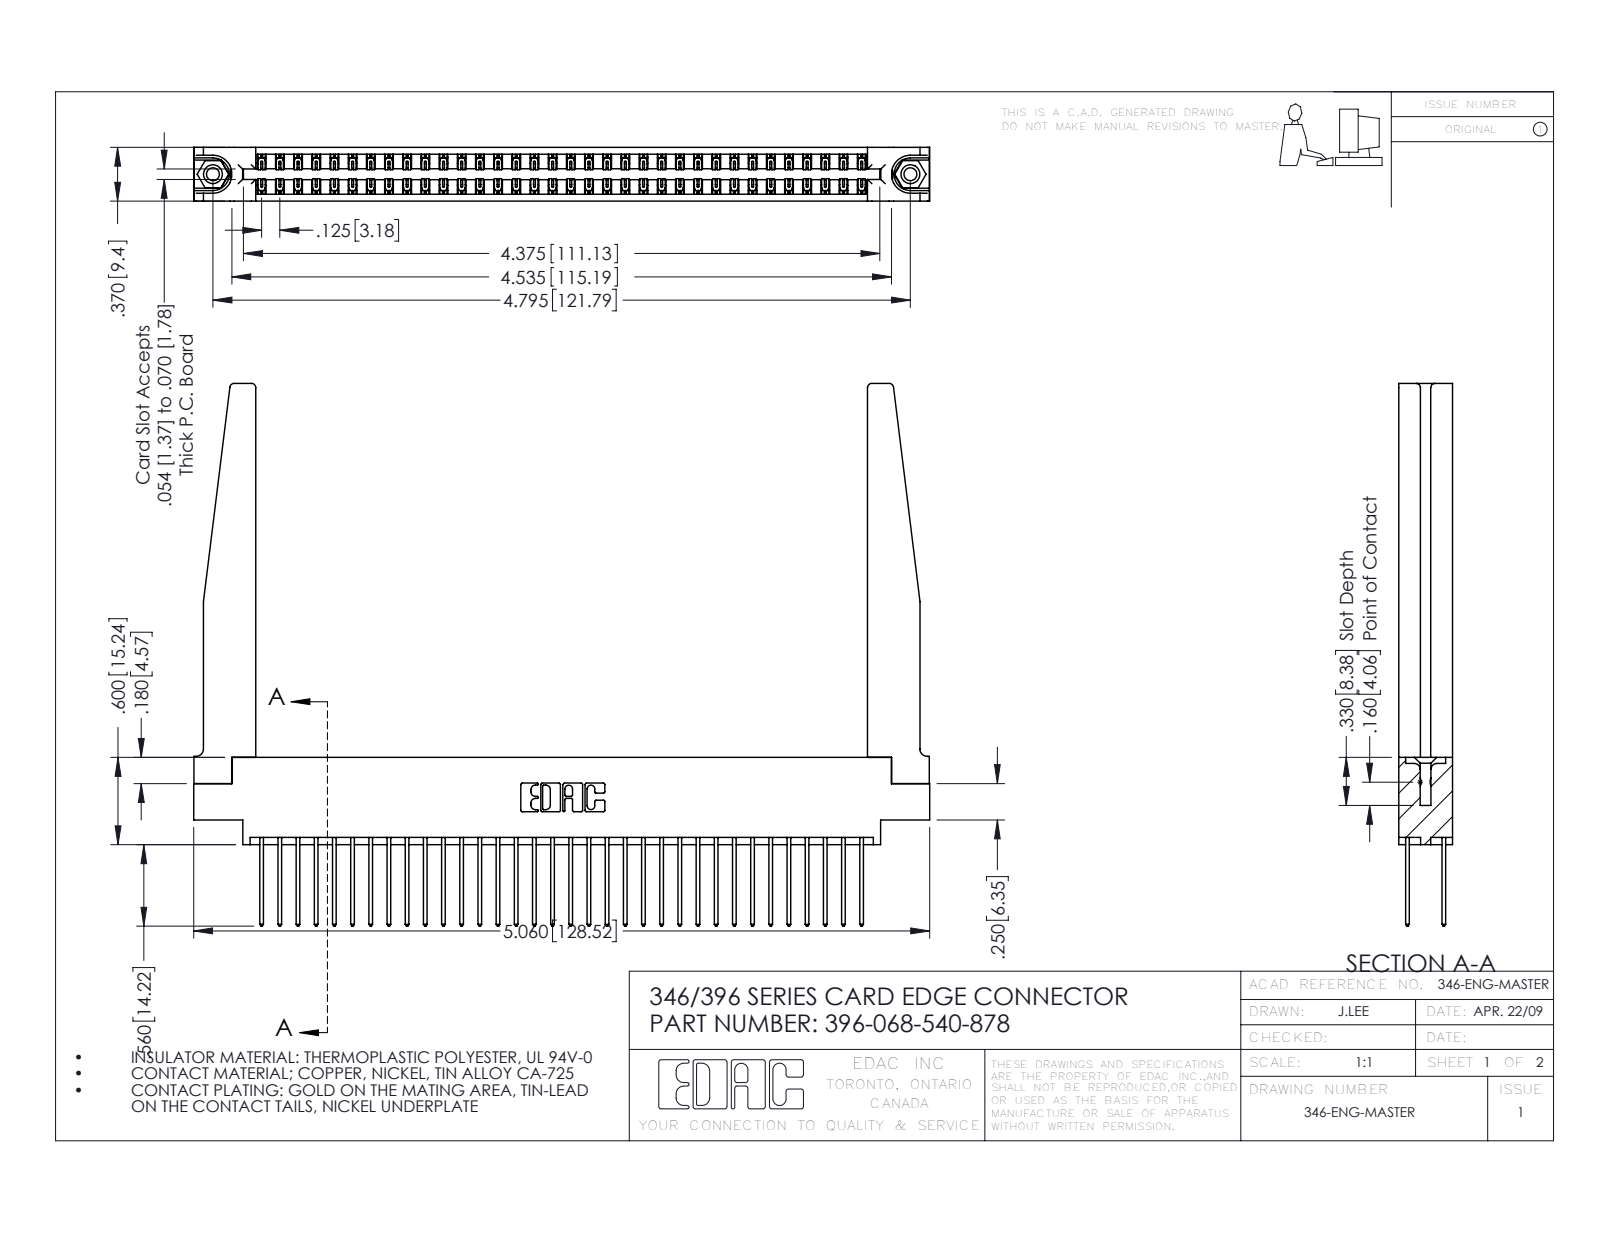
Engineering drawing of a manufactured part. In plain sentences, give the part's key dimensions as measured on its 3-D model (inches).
The part is named "396-068-540-878; 345-250-001_345-250-001-102; 346-220-078_345-220-078; 346 Part_0.170 Offset - 0.156 Dia-TH (+1 more)". Its 3-D file was written by "SolidWorks 2016 (CONFIG_CONTROL_DESIGN)". It is 73 solids with 3896 faces: 2602 planar, 1242 cylindrical and 52 other. Overall it measures 5.06 by 3.73 by 0.37 inches. Its volume is 1.189 cubic inches and its surface area 38.9 square inches. Round holes: 2 of diameter 0.089, 2 of diameter 0.125, 2 of diameter 0.156, 1 of diameter 0.064. Round bosses or shafts: 2 of diameter 0.155. Partial cylindrical surfaces (rounded edges, fillets, slot ends): 102 of radius 0.006, 68 of radius 0.01, 22 of radius 0.01, 8 of radius 0.03, 6 of radius 0.007, 6 of radius 0.031, 3 of radius 0.026, 2 of radius 0.014. The main face-to-face distances are 0.37, 0.048, 0.322, 0.072, 0.25, 0.298, 0.025, 0.148, 0.15, 0.275. The hole center spacings are 0.246, 4.587, 4.795.
